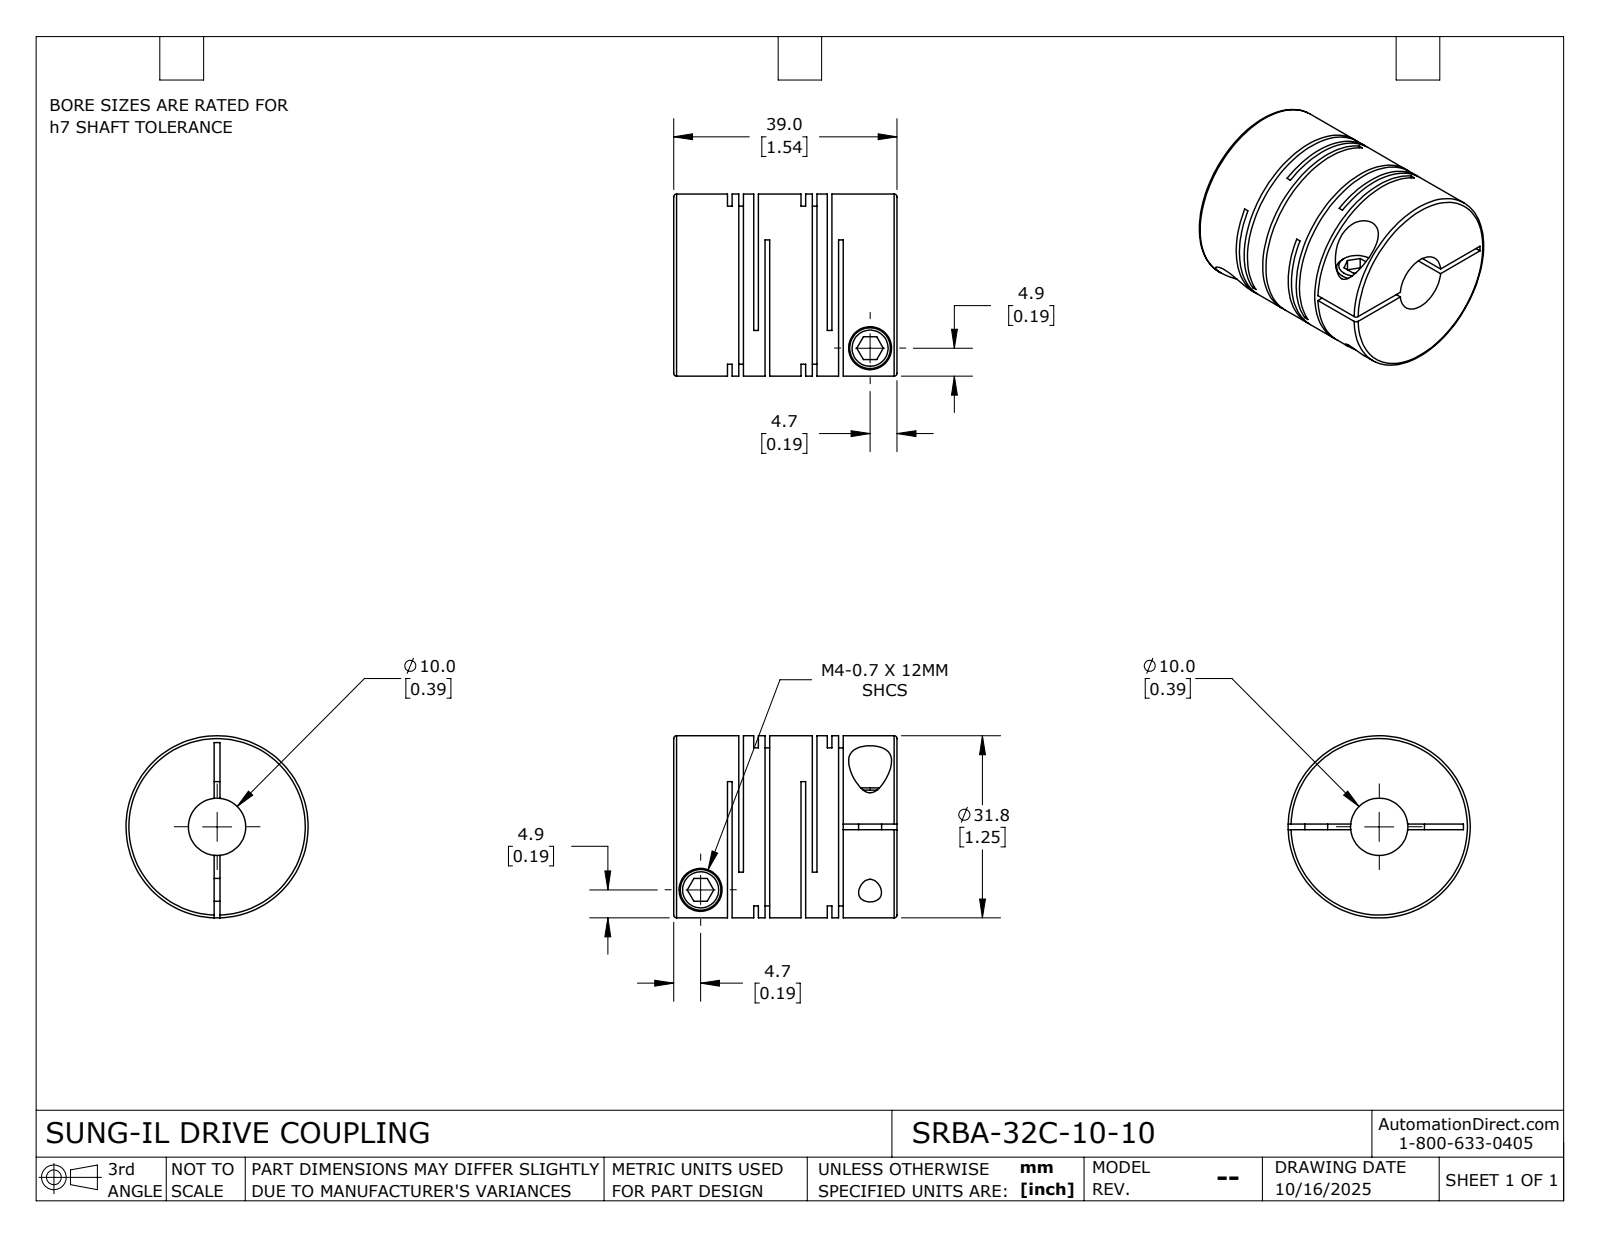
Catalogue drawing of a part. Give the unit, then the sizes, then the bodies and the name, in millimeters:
Units: millimetres
Overall size (bounding box): 39 × 31.8 × 31.8
Round holes (diameter × count): ⌀4 ×2, ⌀7.5 ×2, ⌀10 ×1
Round bosses / shafts (diameter × count): ⌀7.1 ×2, ⌀31.8 ×1
Main face-to-face distances: 0.8, 12.84, 1.98, 4.58, 12.04, 1.18, 10.86, 3.78, 8.26, 2.6
Volume: 23 429 mm³ · Surface area: 16 205 mm²
Bodies: 1 solid, 115 faces (60 planar, 42 cylindrical, 13 other)
Part name (STEP PRODUCT): SRBA-32C-10-10
STEP written by: SolidWorks 2024 (CONFIG_CONTROL_DESIGN)
